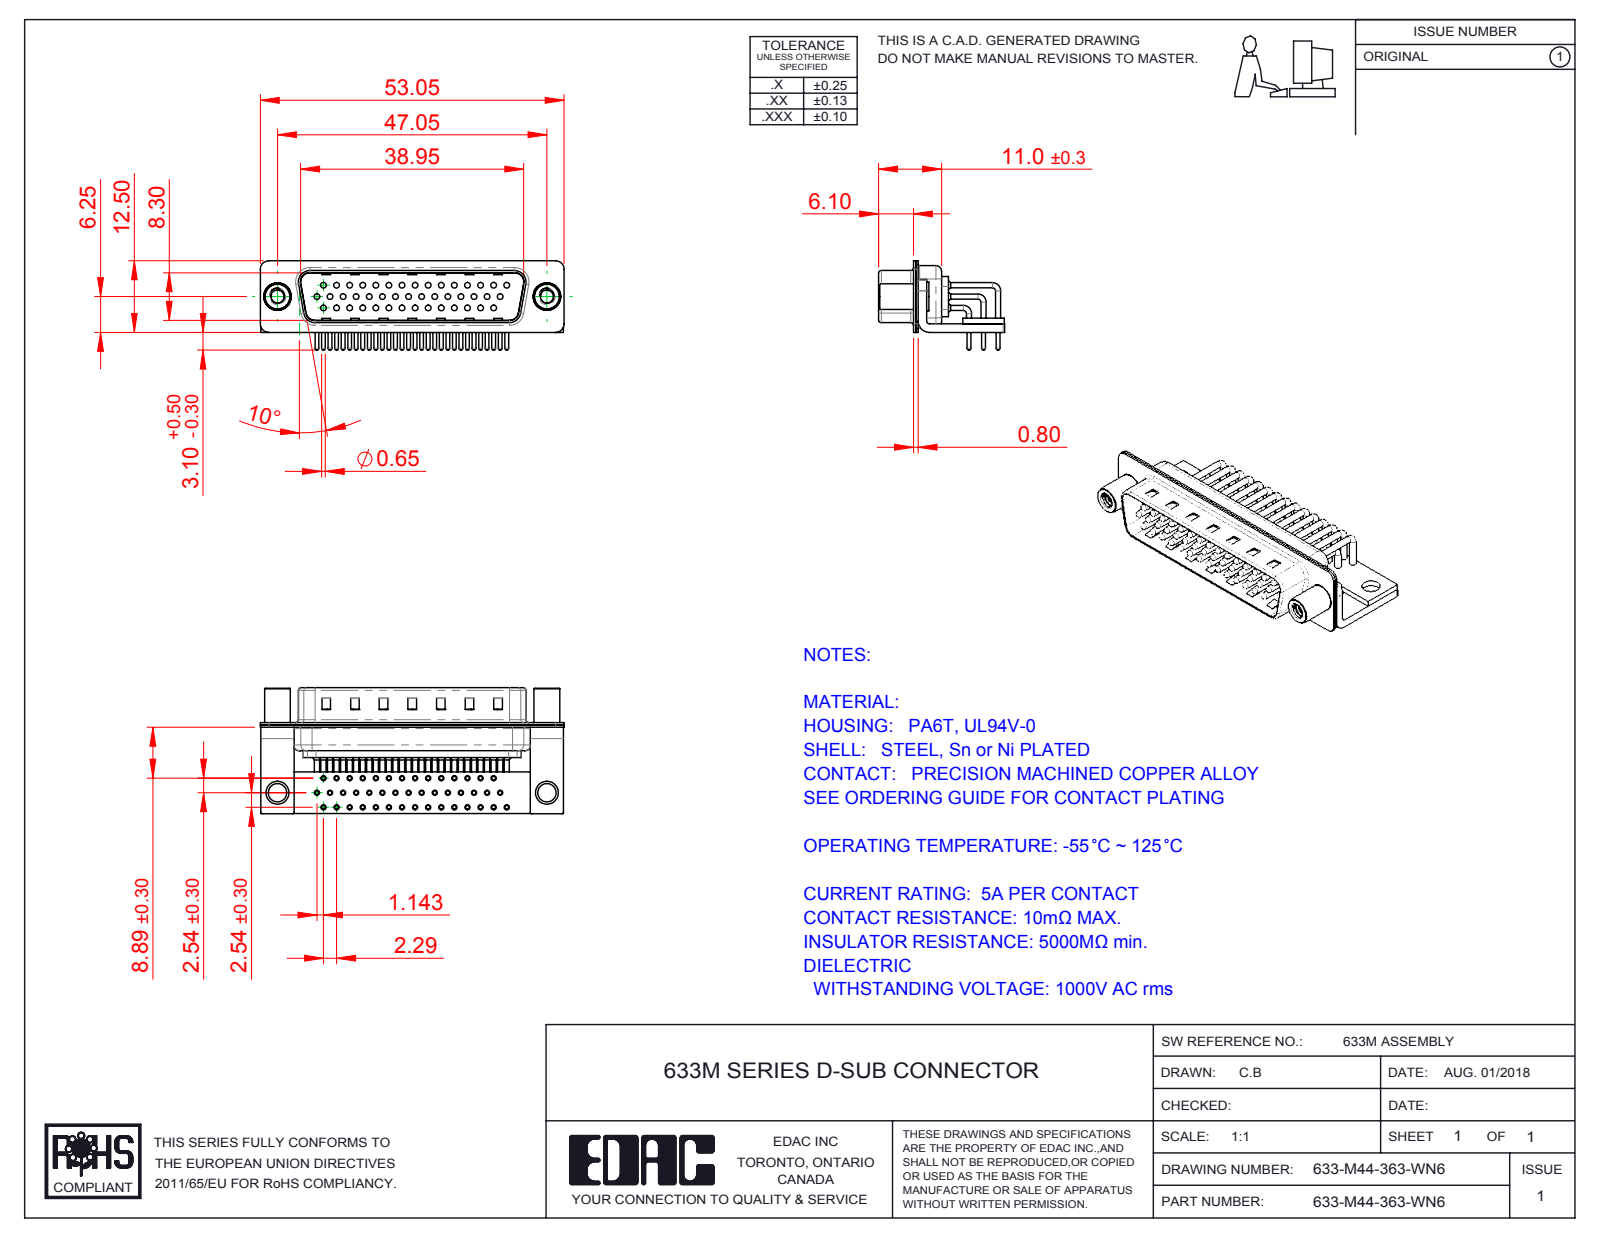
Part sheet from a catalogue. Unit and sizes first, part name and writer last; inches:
Units: inches
Overall size (bounding box): 2.089 × 0.866 × 0.614
Round holes (diameter × count): ⌀0.035 ×44, ⌀0.039 ×44, ⌀0.067 ×44, ⌀0.079 ×44, ⌀0.089 ×2, ⌀0.126 ×2, ⌀0.157 ×2, ⌀0.189 ×2
Round bosses / shafts (diameter × count): ⌀0.035 ×45, ⌀0.059 ×44, ⌀0.026 ×44, ⌀0.197 ×2, ⌀0.193 ×2, ⌀0.177 ×2, ⌀0.039 ×2
Partial cylindrical surfaces — rounded edges, fillets, slot ends (radius × count): R0.04 ×44, R0.01 ×16, R0.059 ×16, R0.079 ×13, R0.02 ×9, R0.063 ×8, R0.024 ×4, R0.026 ×4
Main face-to-face distances: 0.016, 0.033, 0.059, 0.049, 0.039, 0.075, 0.376, 0.031, 0.409, 0.327
Hole centre spacings: 0.09, 0.09, 0.18, 0.27, 0.156, 0.45, 0.324, 0.63
Volume: 0.237 in³ · Surface area: 18.49 in²
Bodies: 52 solids, 5404 faces (3015 planar, 1873 cylindrical, 516 other)
Part name (STEP PRODUCT): 633-M44-363-WN6; 633M Stabilizer Bracket; 633M Stabilizer Board_44 Contacts; 633M 4-40 Threaded Standoff (+6 more)
STEP written by: SolidWorks 2016 (CONFIG_CONTROL_DESIGN)
